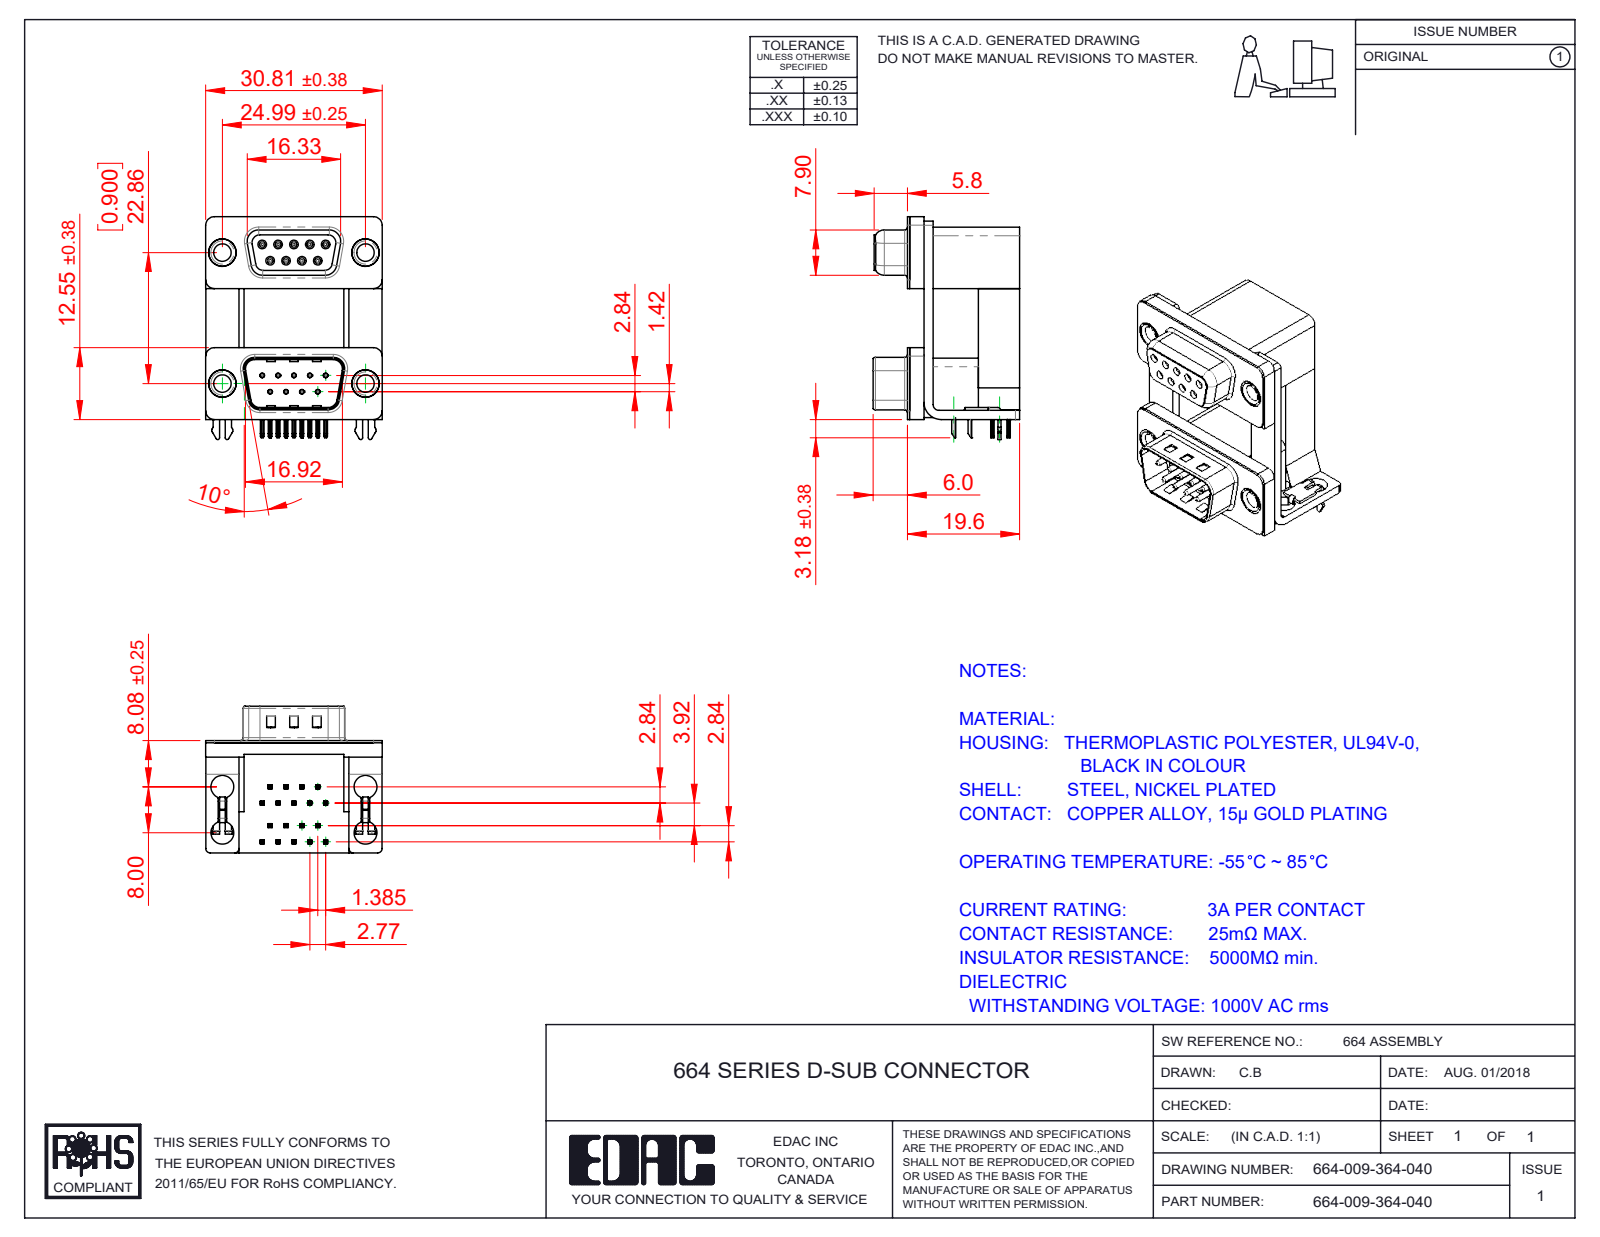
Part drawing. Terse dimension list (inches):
name: 664 Shell Receptacle_09 Contacts; 664 Contact Top Upper_H; 664-009-364-040; 664 Mounting Bracket_2ProngH (+8 more)
written by: SolidWorks 2020 (CONFIG_CONTROL_DESIGN)
unit: in
bodies: 31 solids, 2553 faces (1341 planar, 689 cylindrical, 523 other)
size: 1.532 × 1.213 × 1.008
volume: 0.688 in³; area: 20.41 in²
holes: 18× ⌀0.031, 9× ⌀0.014, 9× ⌀0.035, 8× ⌀0.157, 4× ⌀0.12, 4× ⌀0.138, 4× ⌀0.189, 4× ⌀0.197
bosses: 9× ⌀0.047, 9× ⌀0.03, 4× ⌀0.193, 4× ⌀0.187, 4× ⌀0.152
rounds: 73× R0.004, 42× R0.01, 36× R0.006, 18× R0.005, 18× R0.014, 16× R0.02, 13× R0.059, 10× R0.03
face distances: 0.016, 0.098, 0.657, 0.756, 0.472, 0.374, 0.283, 0.488, 0.063, 0.772
hole spacings: 0.124, 0.907, 0.109, 0.9, 0.926, 1.013, 0.218, 1.025
